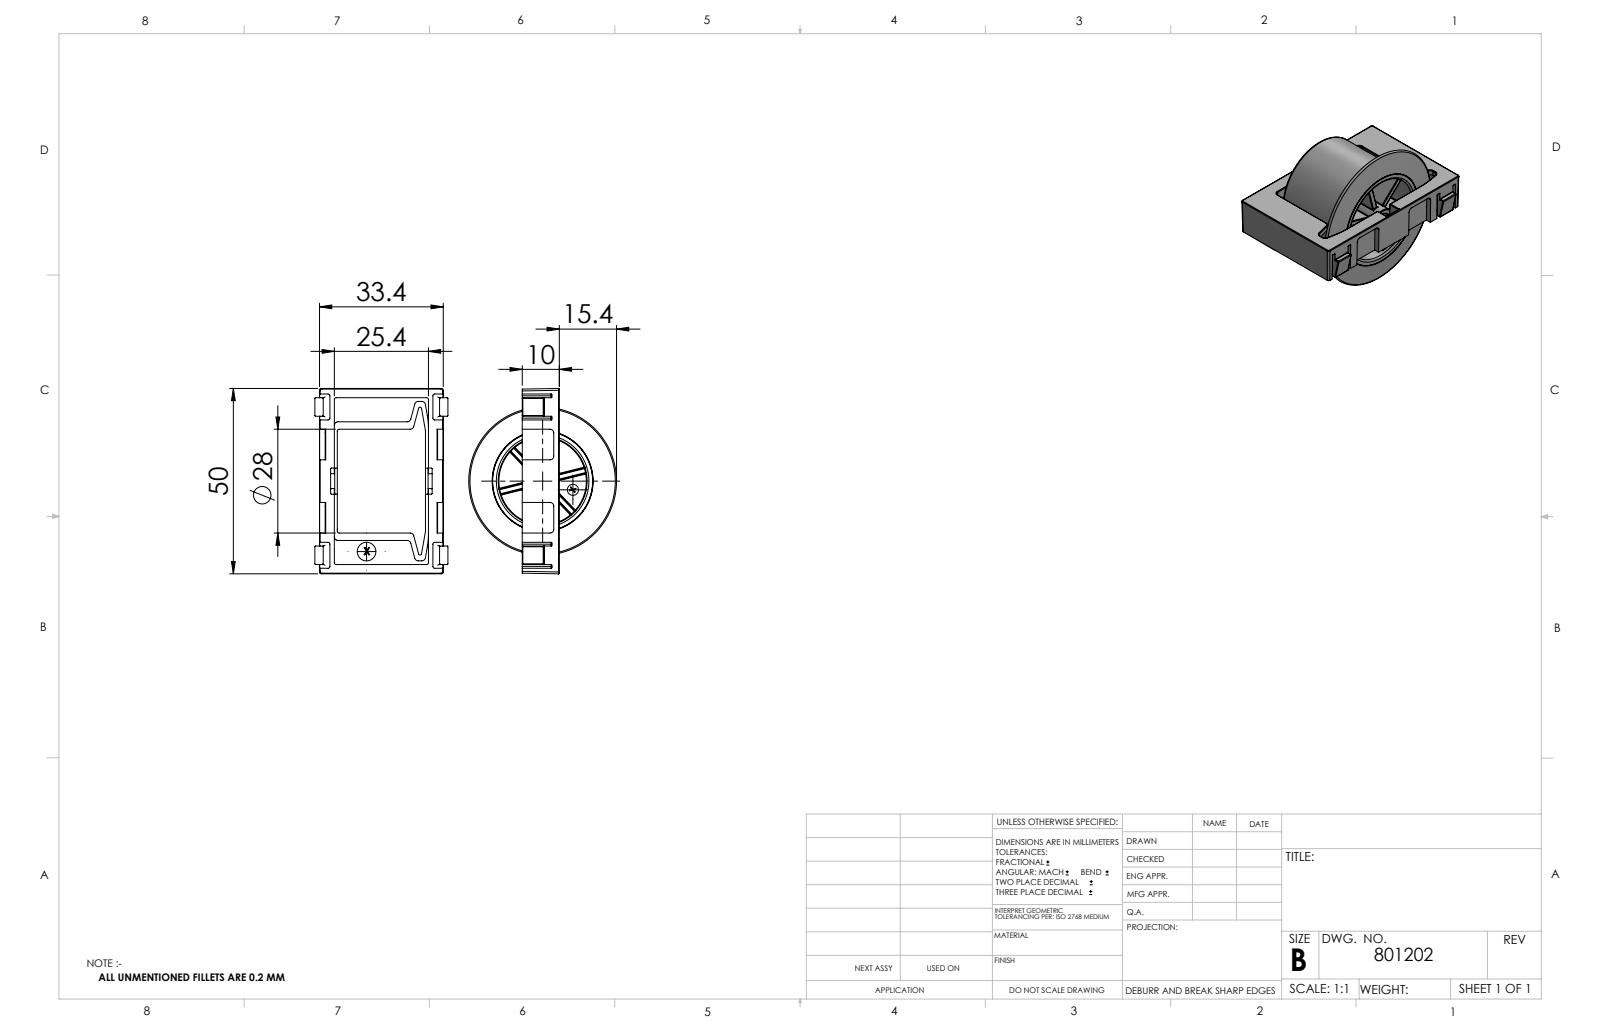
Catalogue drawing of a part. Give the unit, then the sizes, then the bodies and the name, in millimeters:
Units: millimetres
Overall size (bounding box): 49.99 × 39.89 × 35.9
Round holes (diameter × count): ⌀4.2 ×1, ⌀24 ×1
Round bosses / shafts (diameter × count): ⌀28 ×1, ⌀7 ×1, ⌀5.03 ×1, ⌀4 ×1, ⌀3 ×1
Partial cylindrical surfaces — rounded edges, fillets, slot ends (radius × count): R0.2 ×159, R0.5 ×22, R1 ×12, R0.1 ×2, R20 ×2, R2.05 ×1
Main face-to-face distances: 1.5, 11.8, 13.6, 1.8, 10, 1.51, 25.4, 14.8, 8.5, 2
Volume: 12 827 mm³ · Surface area: 14 072 mm²
Bodies: 3 solids, 805 faces (172 planar, 291 cylindrical, 342 other)
Part name (STEP PRODUCT): 801202_c_1
STEP written by: SolidWorks 2014 (CONFIG_CONTROL_DESIGN)
